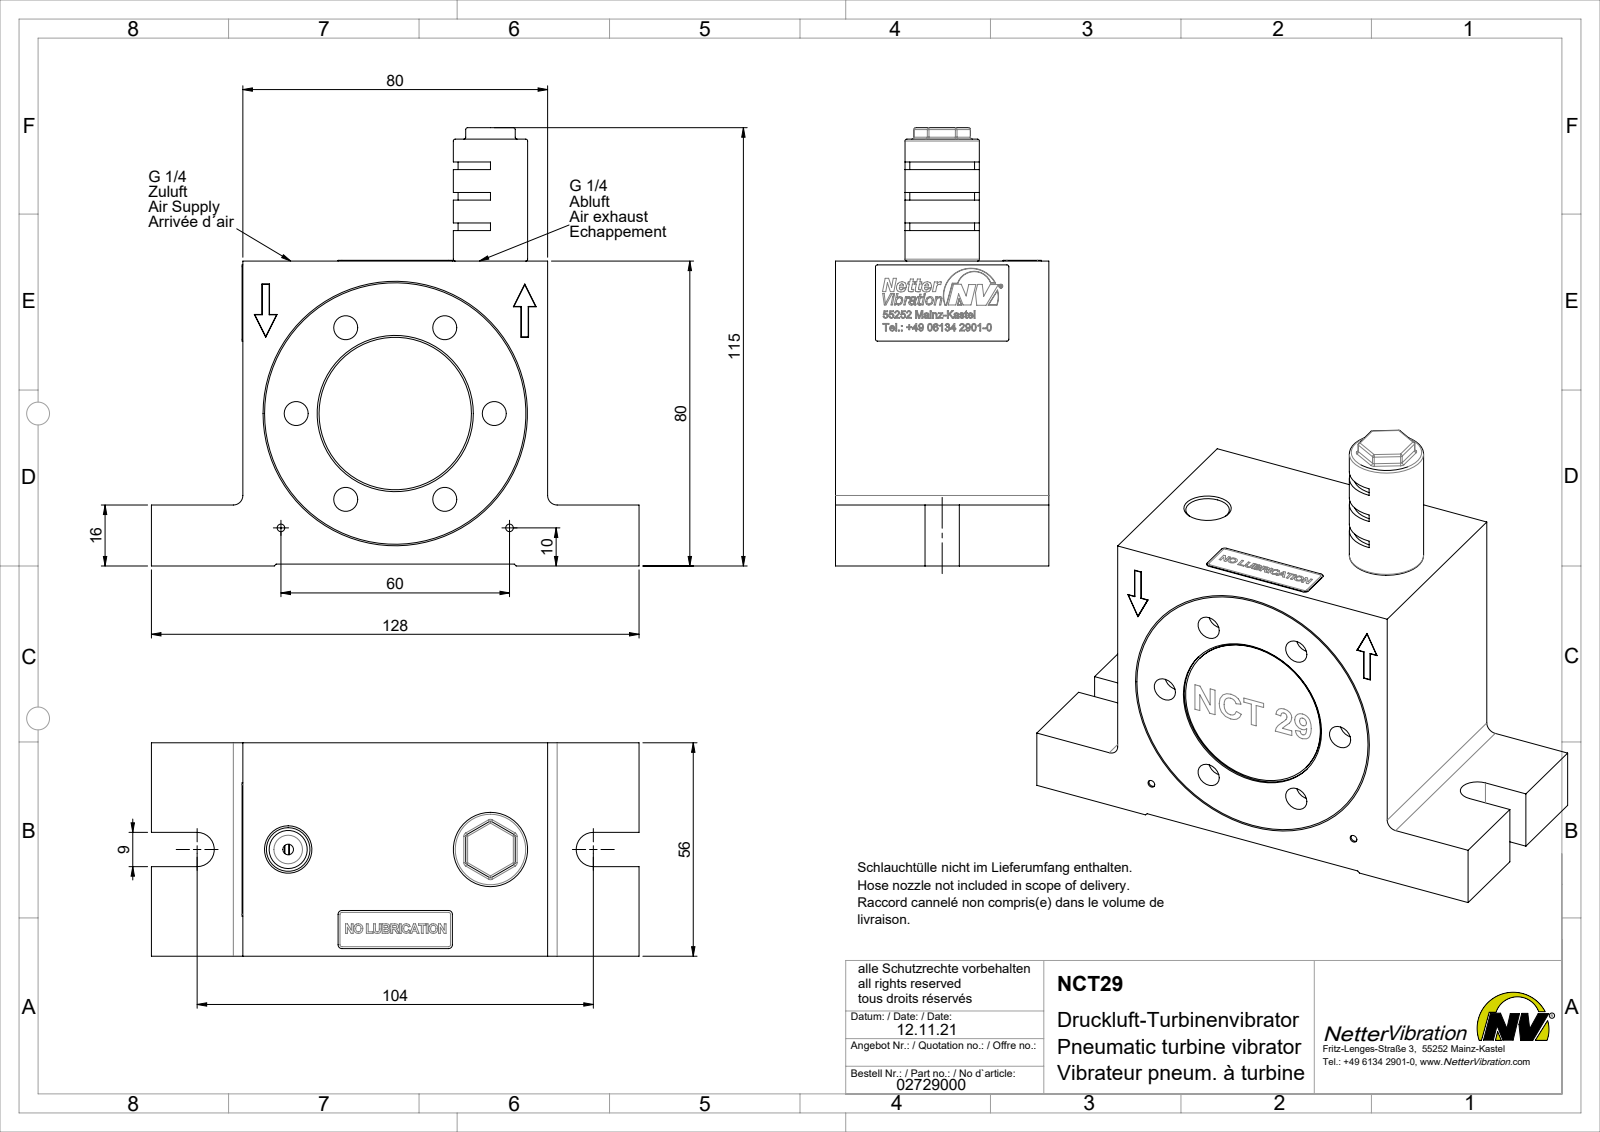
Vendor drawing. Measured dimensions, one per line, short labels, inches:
name: NCT 29 Turbinenvibrator #02729000
written by: SolidWorks 2015 (AUTOMOTIVE_DESIGN)
unit: in
bodies: 6 solids, 336 faces (204 planar, 75 cylindrical, 57 other)
size: 5.039 × 4.528 × 2.205
volume: 26.55 in³; area: 93.73 in²
holes: 6× ⌀0.248, 2× ⌀0.079, 2× ⌀0.451, 1× ⌀1.614, 1× ⌀2.669
bosses: 1× ⌀2.756, 1× ⌀2.668, 1× ⌀2.581, 1× ⌀1.575, 1× ⌀0.768, 1× ⌀0.518
rounds: 22× R0.02, 4× R0.039, 2× R0.098, 2× R0.177, 1× R0.335
face distances: 3.15, 0.02, 2.205, 0.63, 0.315, 0.335, 1.89, 0.65, 1.555, 3.13
hole spacings: 1.024, 1.773, 0.731, 1.192, 1.67, 1.719, 1.773, 2.048
